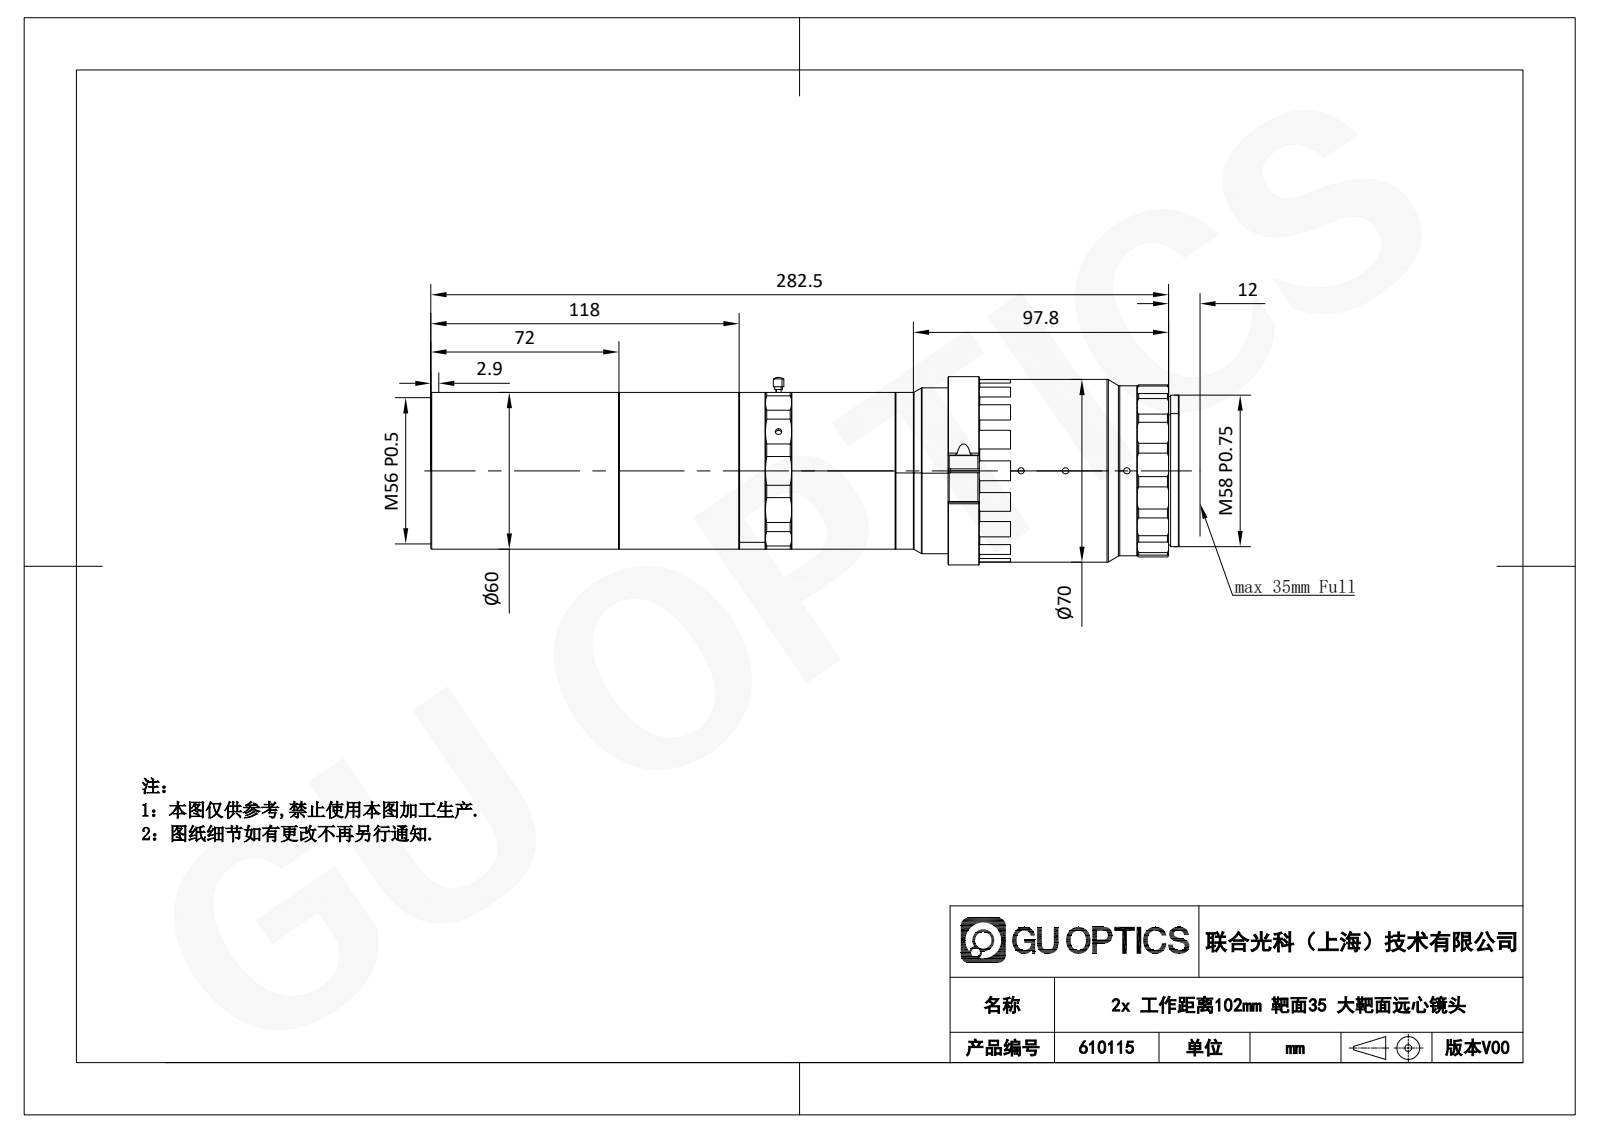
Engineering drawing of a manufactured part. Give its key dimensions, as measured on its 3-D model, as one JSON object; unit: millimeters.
{"part_name": "DTCA35F-22-G-M58-AL", "step_written_by": "SolidWorks 2017 (CONFIG_CONTROL_DESIGN)", "units": "millimeters", "bodies": {"solids": 1, "faces": 490, "planar": 120, "cylindrical": 176, "other": 194}, "overall_size": [286.5, 78.49, 72], "volume_mm3": 816106, "surface_area_mm2": 77621, "round_holes": [[2.4, 9], [2.5, 3], [2.2, 1], [3.4, 1], [4.5, 1], [52.5, 1], [55.5, 1], [58, 1], [63.5, 1], [68.3, 1]], "round_bosses_or_shafts": [[72, 1], [70, 1], [68, 1], [67, 1], [65, 1], [61.4, 1], [61, 1], [60, 1]], "partial_cylinders_radius": [[15, 34], [1, 2], [4, 1], [33, 1], [42.5, 1]], "face_to_face_distances": [84.5, 20.1, 60, 104.6, 12, 72.5, 64.5, 24, 20, 84.6], "hole_center_spacings": [17, 23.5, 40.5, 80.66]}
